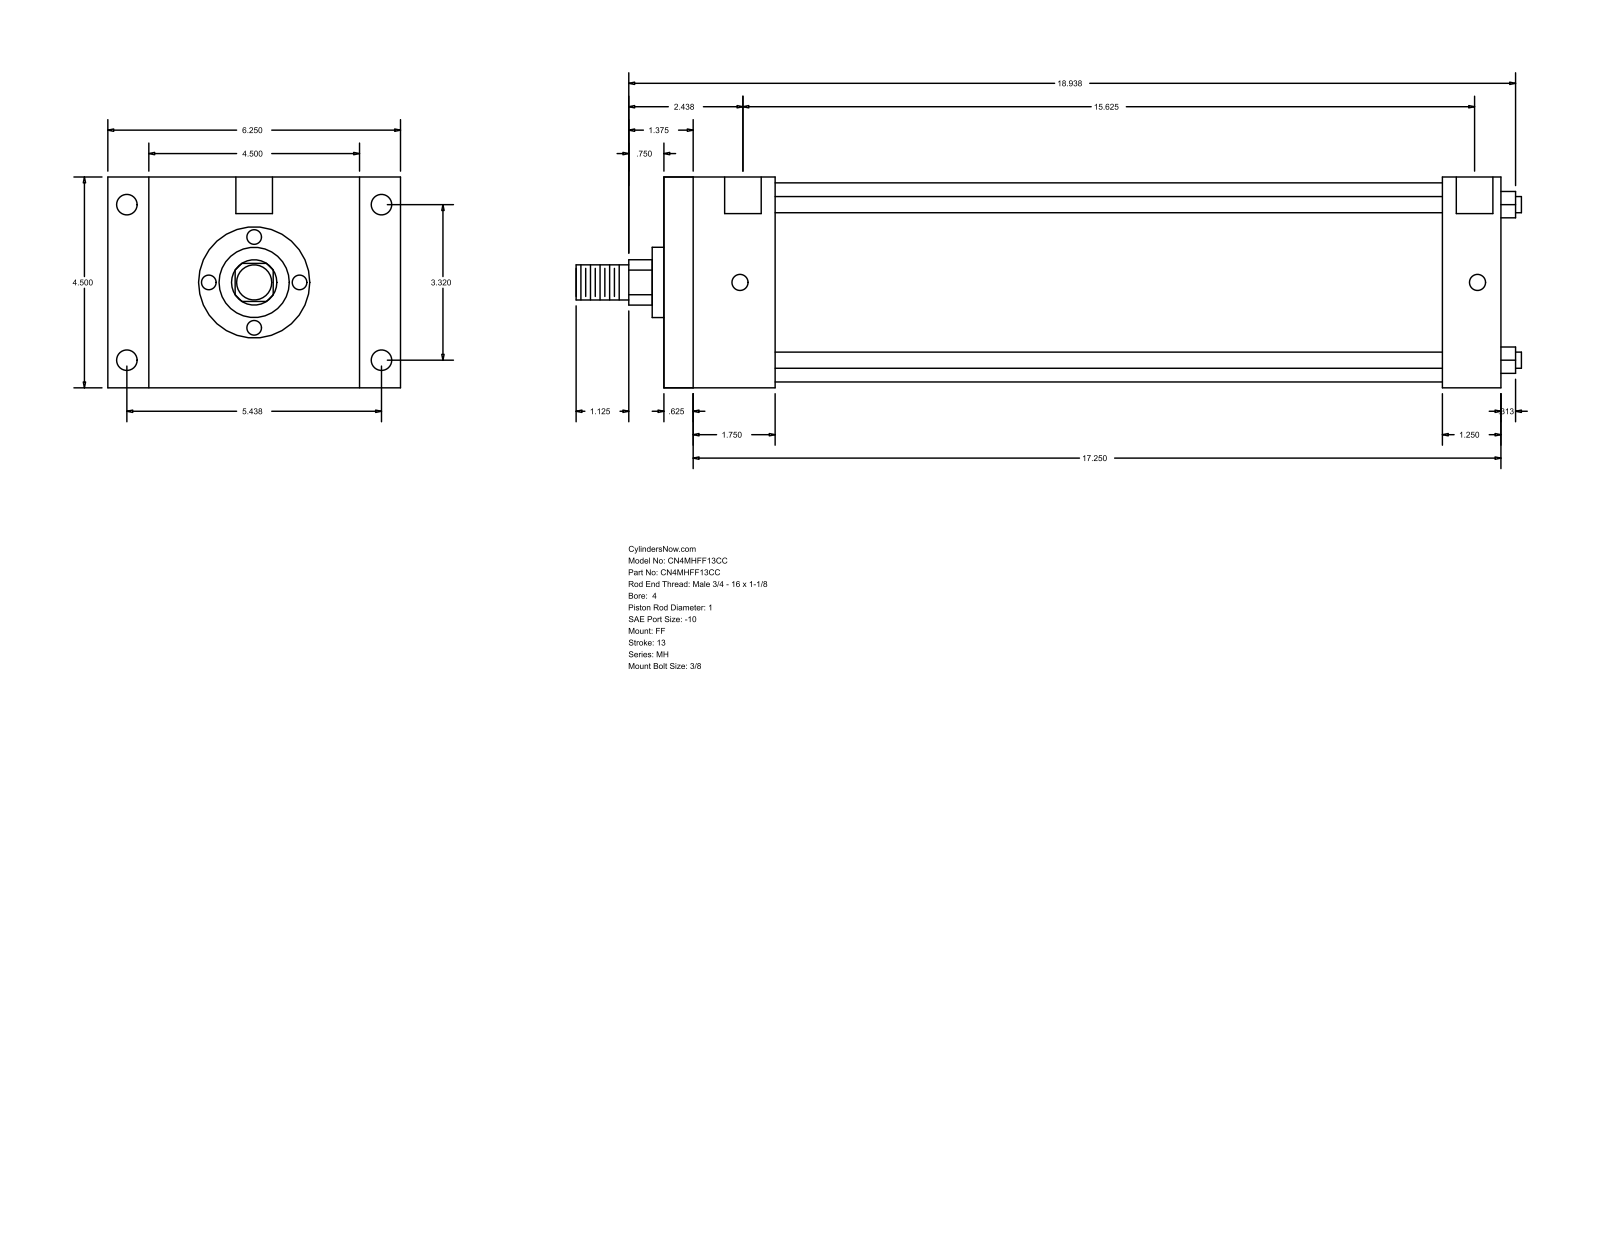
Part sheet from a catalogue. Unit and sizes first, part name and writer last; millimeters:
Units: millimetres
Overall size (bounding box): 512.76 × 158.75 × 114.3
Round holes (diameter × count): ⌀8.73 ×4, ⌀11.13 ×4, ⌀19.84 ×2
Round bosses / shafts (diameter × count): ⌀8.76 ×4, ⌀107.95 ×1, ⌀38.1 ×1, ⌀25.4 ×1, ⌀19.05 ×1
Partial cylindrical surfaces — rounded edges, fillets, slot ends (radius × count): R12.29 ×1
Main face-to-face distances: 114.3, 454.02, 15.87, 438.15, 60.33, 44.46, 393.69, 422.27, 406.4, 361.94
Hole centre spacings: 84.32, 138.12, 161.82, 400.05, 1.58, 1.59, 396.88, 398.46
Bodies: 0 solids, 92 faces (64 planar, 28 cylindrical, 0 other)
Part name (STEP PRODUCT): MH_FF__0400_1
STEP written by: GSSL Pune (CONFIG_CONTROL_DESIGN)
